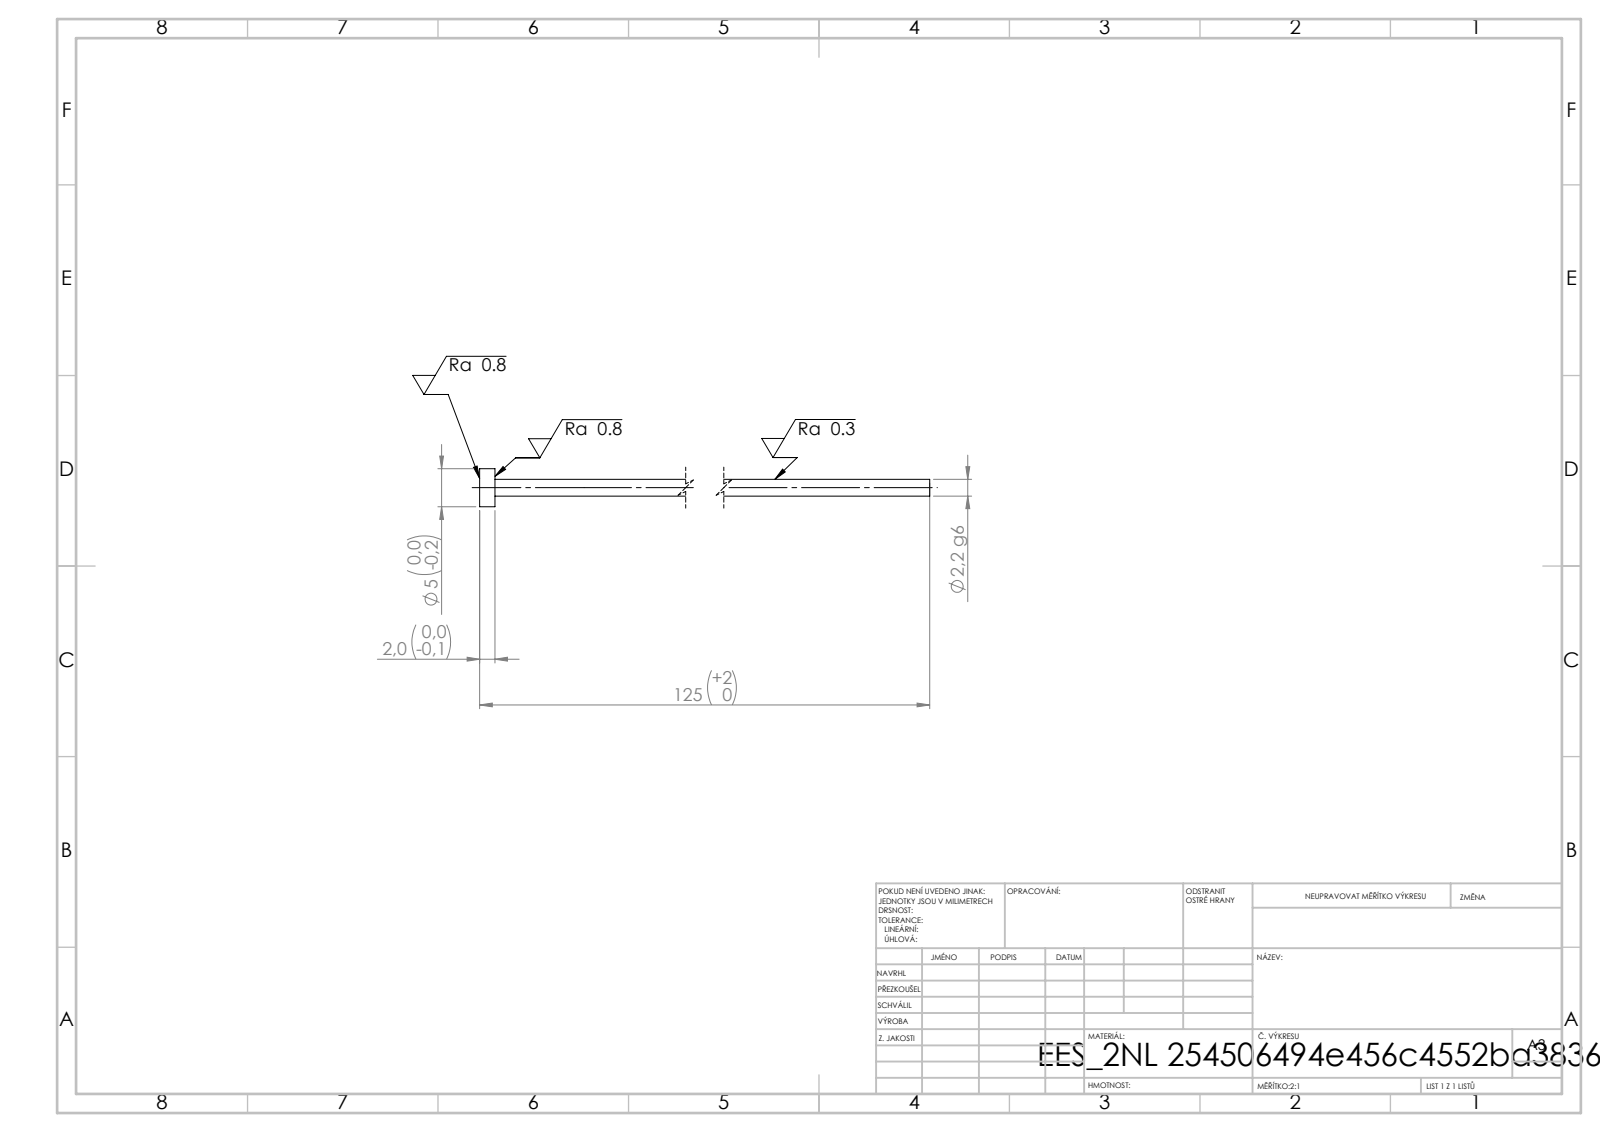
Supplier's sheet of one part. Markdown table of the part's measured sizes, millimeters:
| quantity | value |
| --- | --- |
| STEP written by | SolidWorks 2019 (CONFIG_CONTROL_DESIGN) |
| units | millimeters |
| bodies | 1 solid, 7 faces (3 planar, 4 cylindrical, 0 other) |
| overall size | 125 × 5 × 5 |
| volume | 507 mm³ |
| surface area | 921 mm² |
| round bosses / shafts (diameter × count) | 5 × 1, 2.2 × 1 |
| main face-to-face distances | 2, 125, 123 |
